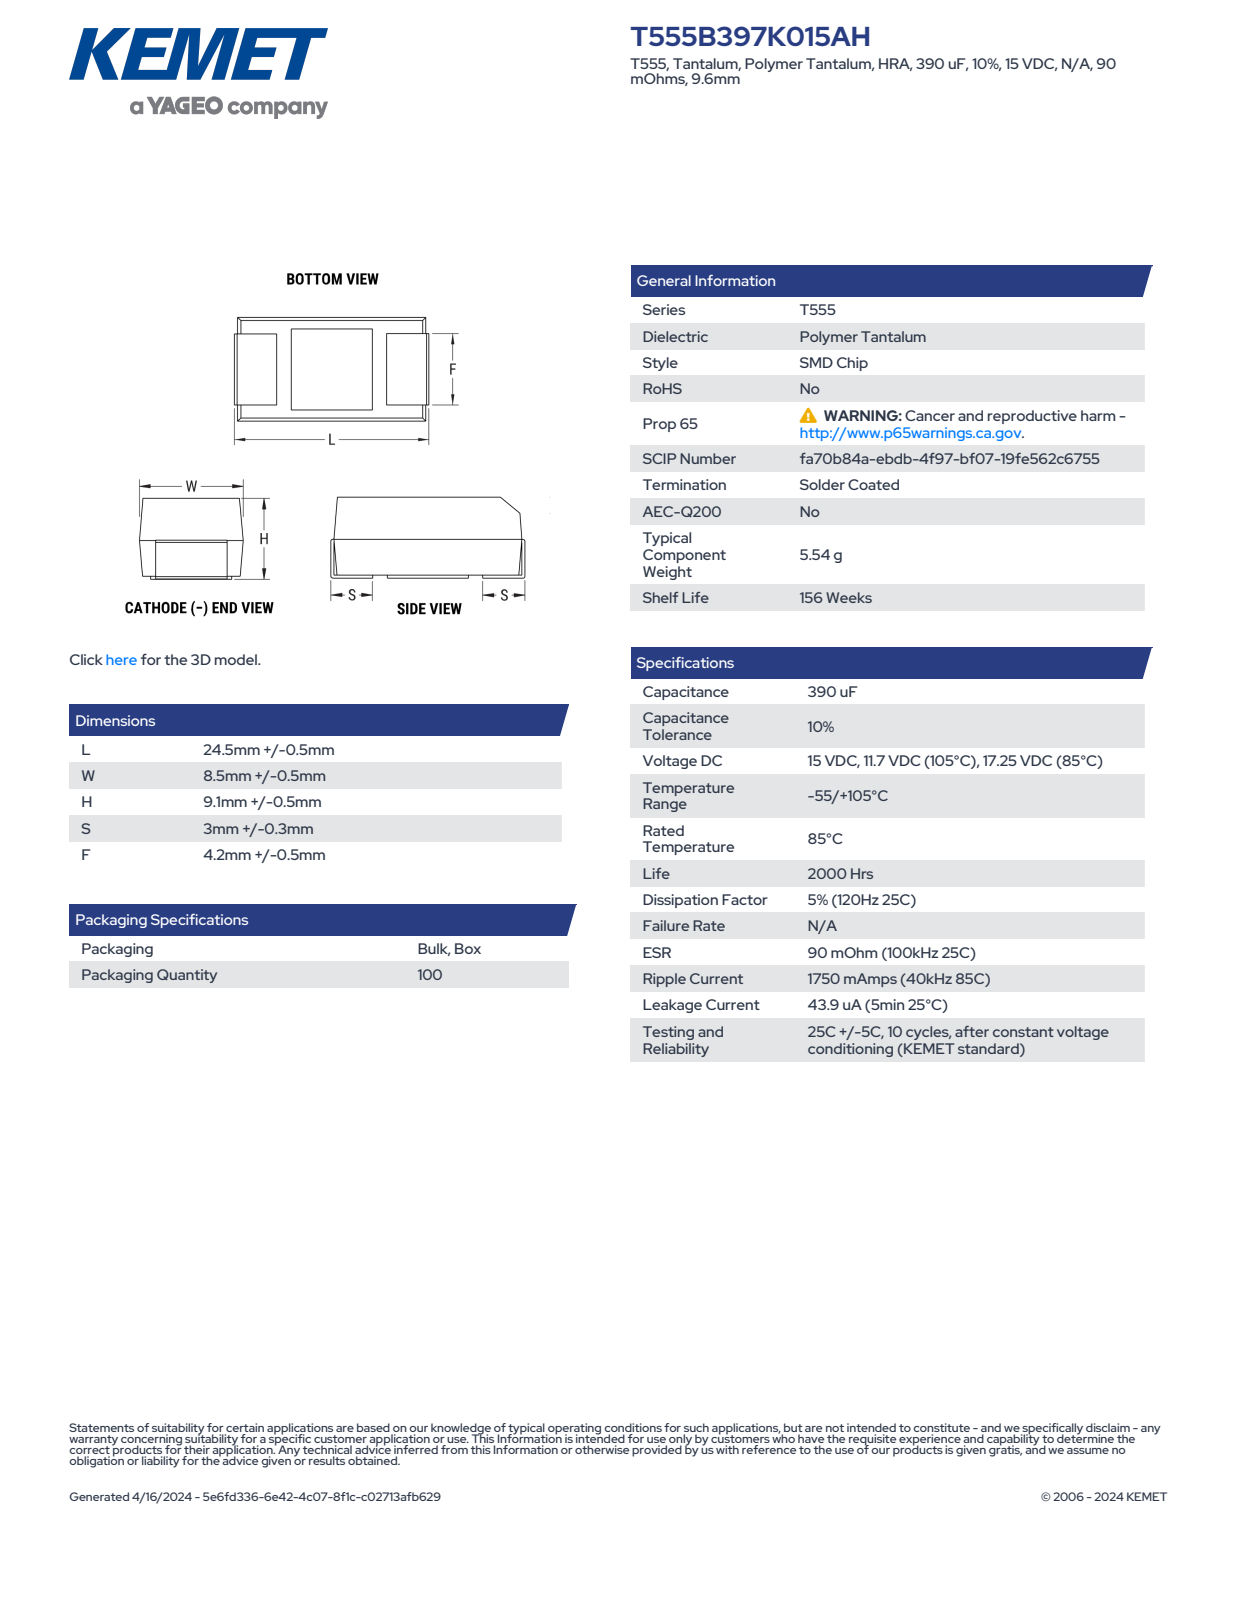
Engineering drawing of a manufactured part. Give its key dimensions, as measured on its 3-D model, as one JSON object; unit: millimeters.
{"part_name": "CTSM_Case_Anode_38; CTSM_Case_Top_38; CTSM_Case_Cathode_38; CTSM_B_L25.00W9H9.60S3F4.2 (+1 more)", "step_written_by": "SolidWorks 2014 (AUTOMOTIVE_DESIGN)", "units": "millimeters", "bodies": {"solids": 7, "faces": 89, "planar": 85, "cylindrical": 4, "other": 0}, "overall_size": [25, 9.6, 9], "volume_mm3": 1987, "surface_area_mm2": 1602, "face_to_face_distances": [4.65, 9.47, 4.82, 8.97, 8.96, 24.64, 24.87, 4.78, 9.6, 24.74]}
